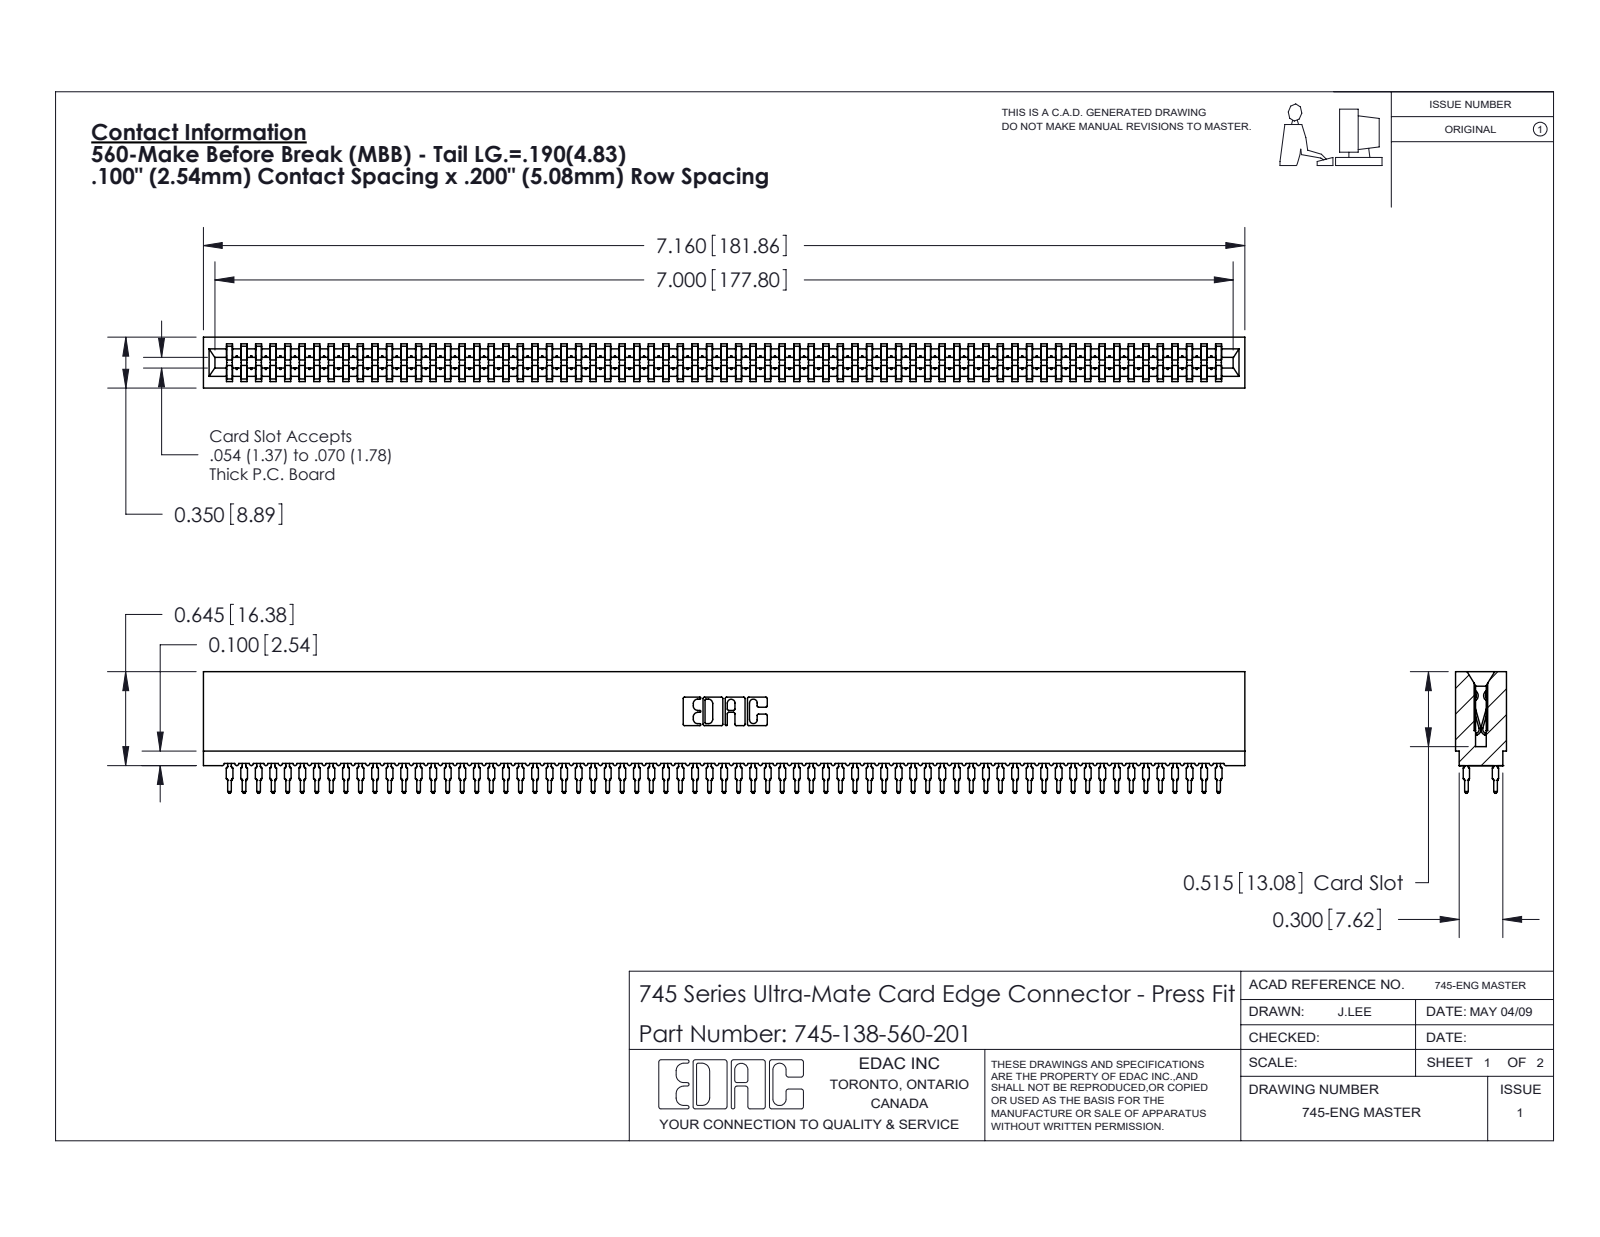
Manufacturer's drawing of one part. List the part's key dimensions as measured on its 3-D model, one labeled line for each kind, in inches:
Part name (STEP PRODUCT): 745-292-001_560; 745 Part_Insulator Option - 01; 745-138-560-201
STEP written by: SolidWorks 2020 (CONFIG_CONTROL_DESIGN)
Units: inches
Bodies: 139 solids, 13688 faces (7093 planar, 3007 cylindrical, 3588 other)
Overall size (bounding box): 7.16 × 0.836 × 0.35
Volume: 1.021 in³ · Surface area: 57.05 in²
Partial cylindrical surfaces — rounded edges, fillets, slot ends (radius × count): R0.021 ×276, R0.015 ×138, R0.01 ×22, R0.005 ×8, R0.011 ×8, R0.007 ×6, R0.031 ×6, R0.026 ×3
Main face-to-face distances: 0.35, 0.063, 0.287, 0.045, 0.305, 0.018, 0.243, 0.138, 0.212, 0.093
